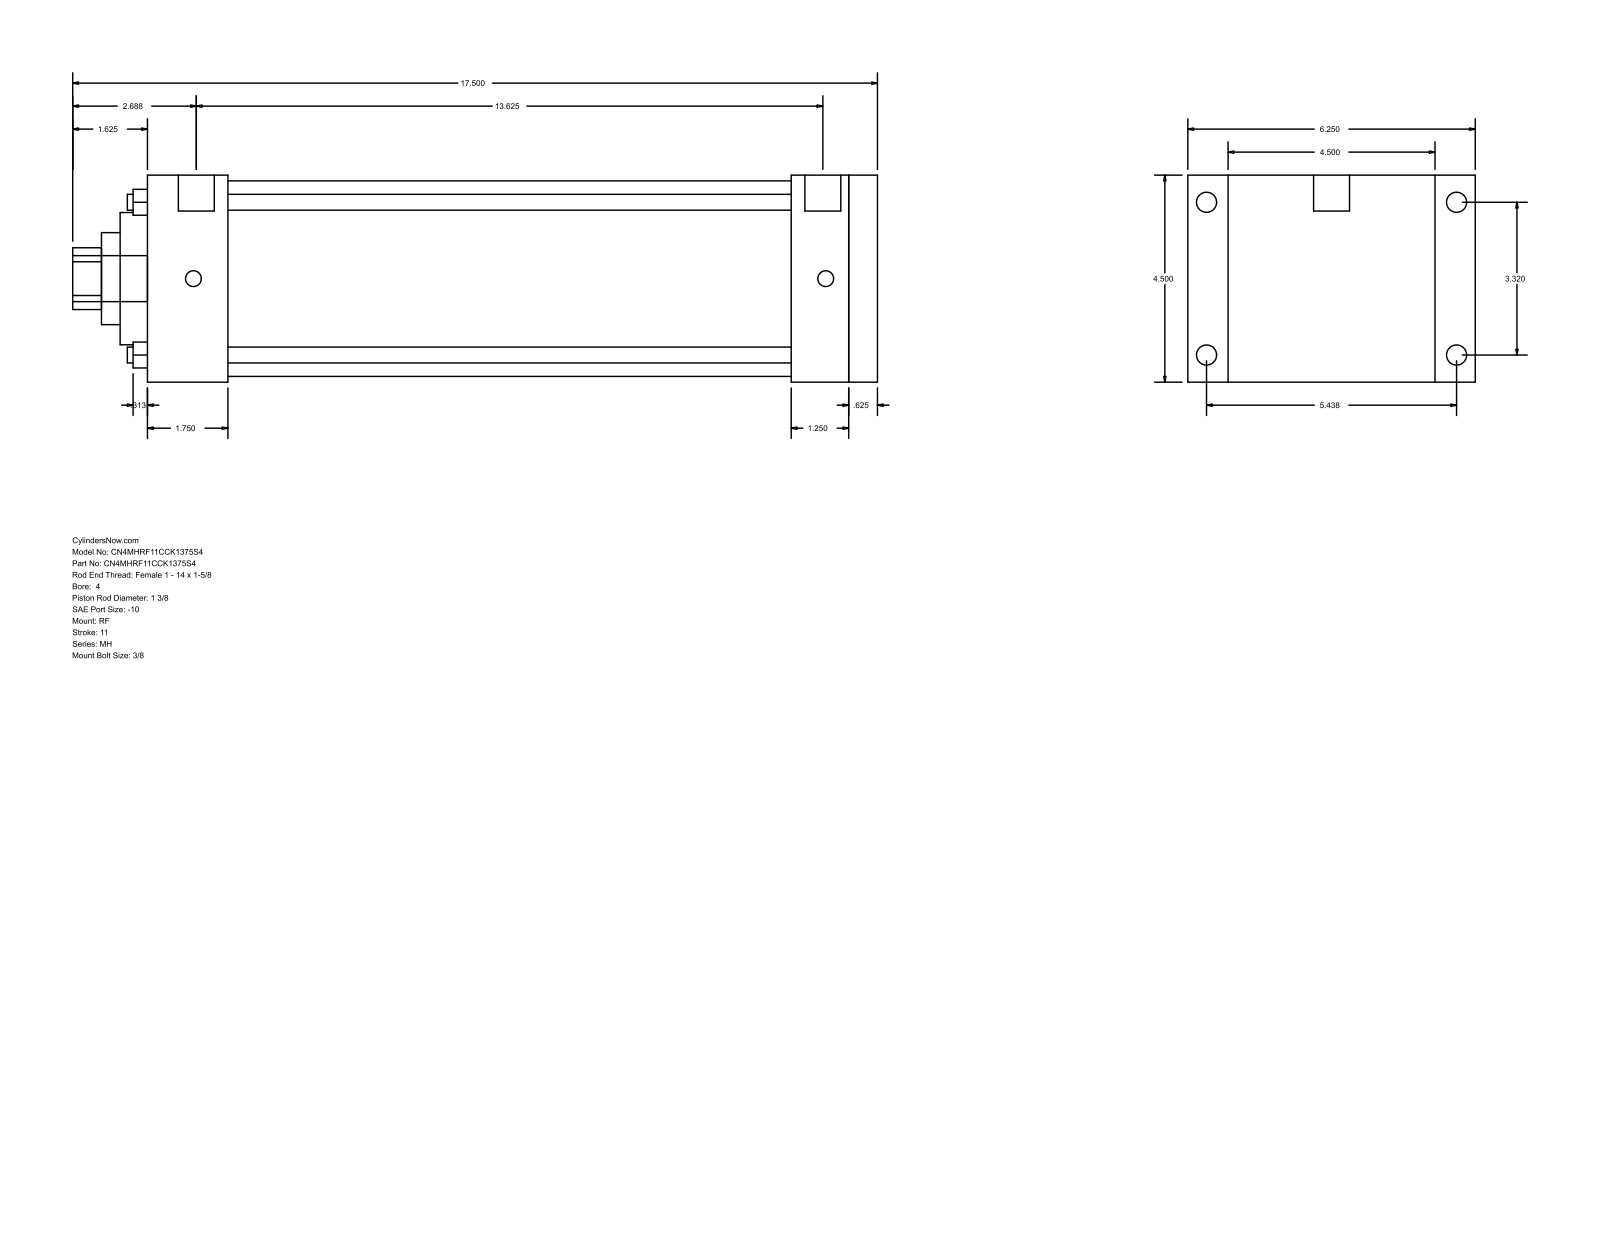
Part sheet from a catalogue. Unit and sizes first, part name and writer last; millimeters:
Units: millimetres
Overall size (bounding box): 444.5 × 158.75 × 114.3
Round holes (diameter × count): ⌀8.76 ×4, ⌀34.92 ×1, ⌀50.8 ×1, ⌀73.03 ×1, ⌀107.95 ×1
Round bosses / shafts (diameter × count): ⌀11.13 ×4, ⌀8.73 ×4, ⌀19.84 ×2, ⌀25.4 ×1
Partial cylindrical surfaces — rounded edges, fillets, slot ends (radius × count): R17.06 ×1
Main face-to-face distances: 114.3, 403.23, 15.88, 387.35, 44.45, 342.9, 358.78, 355.61, 311.16, 31.74
Hole centre spacings: 59.62, 84.32, 119.25
Bodies: 0 solids, 94 faces (65 planar, 29 cylindrical, 0 other)
Part name (STEP PRODUCT): MH_RF__0400_1.375
STEP written by: GSSL Pune (CONFIG_CONTROL_DESIGN)
